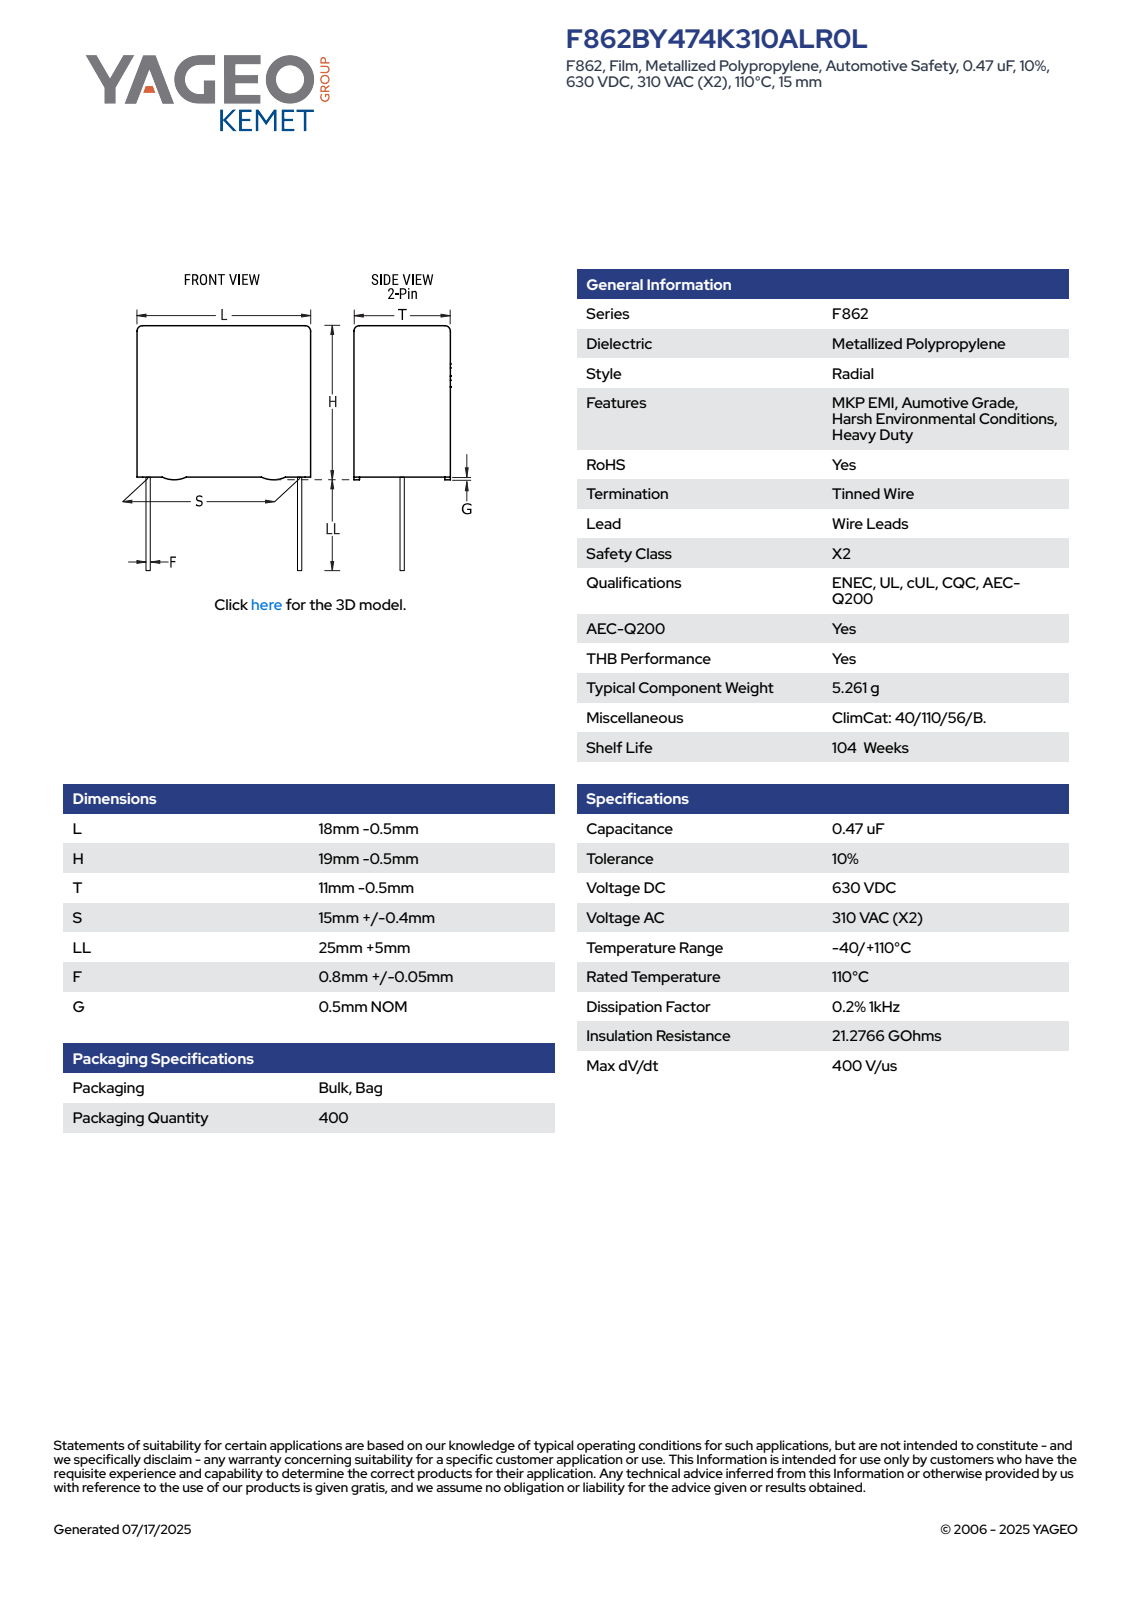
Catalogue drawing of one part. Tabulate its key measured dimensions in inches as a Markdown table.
| quantity | value |
| --- | --- |
| part name | CFR_RBG_18X19X11_L17.5H18.5T10.5S15LL30F0.85G0.5 |
| STEP written by | SolidWorks 2014 (AUTOMOTIVE_DESIGN) |
| units | inches |
| bodies | 4 solids, 89 faces (81 planar, 8 cylindrical, 0 other) |
| overall size | 1.909 × 0.689 × 0.414 |
| volume | 0.204 in³ |
| surface area | 2.437 in² |
| round bosses / shafts (diameter × count) | 0.033 × 2 |
| partial cylindrical surfaces (radius × count) | 0.02 × 4 |
| main face-to-face distances | 0.413, 0.689, 0.709, 0.414, 0.02, 0.728, 0.024, 0.39, 0.024, 0.366 |
